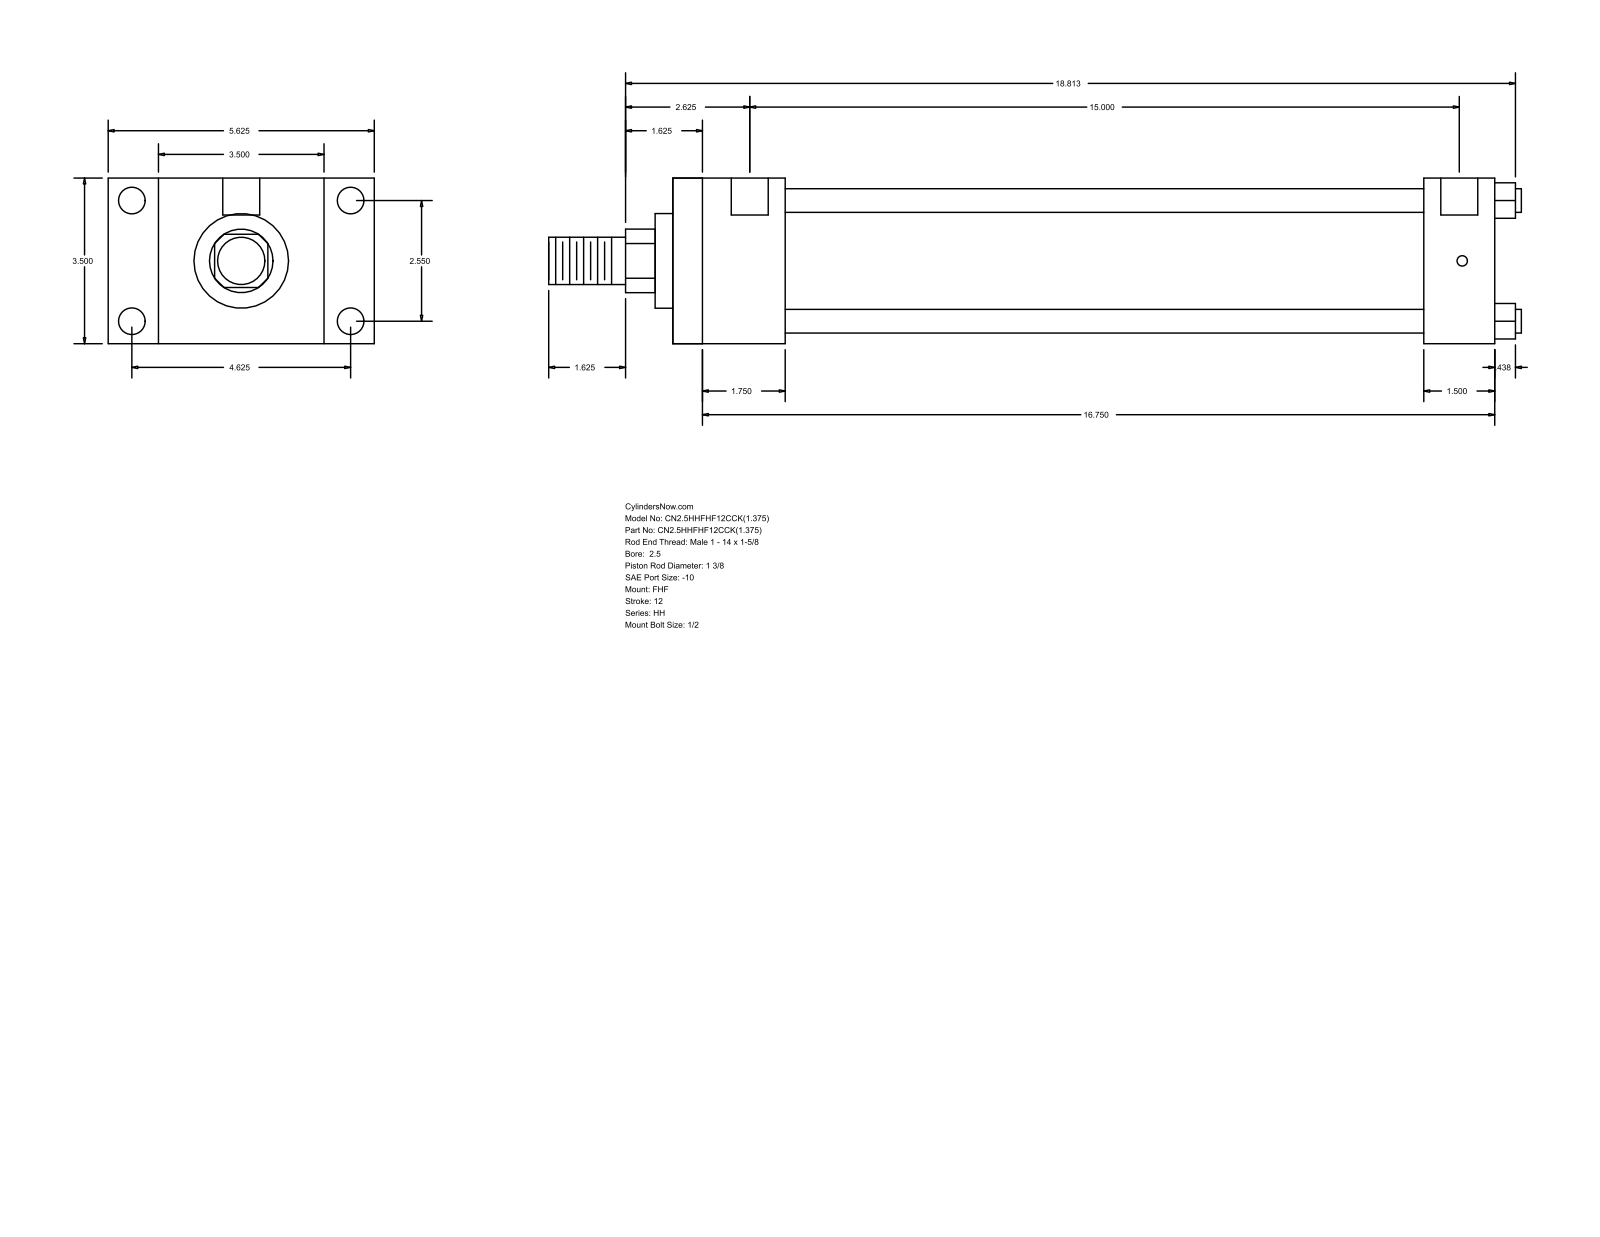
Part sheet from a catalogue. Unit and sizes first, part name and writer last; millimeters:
Units: millimetres
Overall size (bounding box): 522.29 × 142.88 × 88.9
Round holes (diameter × count): ⌀5.56 ×4, ⌀14.3 ×4, ⌀19.84 ×2
Round bosses / shafts (diameter × count): ⌀12.7 ×4, ⌀73.03 ×1, ⌀50.8 ×1, ⌀34.92 ×1, ⌀25.4 ×1
Partial cylindrical surfaces — rounded edges, fillets, slot ends (radius × count): R17.06 ×1
Main face-to-face distances: 88.9, 60.32, 26.99, 115.89, 441.33, 381.01, 142.88, 403.22, 342.9, 38.11
Hole centre spacings: 1.58, 64.76, 117.48, 134.15, 382.59, 384.17, 381.01
Bodies: 0 solids, 88 faces (60 planar, 28 cylindrical, 0 other)
Part name (STEP PRODUCT): HH_FHF__0250_1.375
STEP written by: GSSL Pune (CONFIG_CONTROL_DESIGN)
